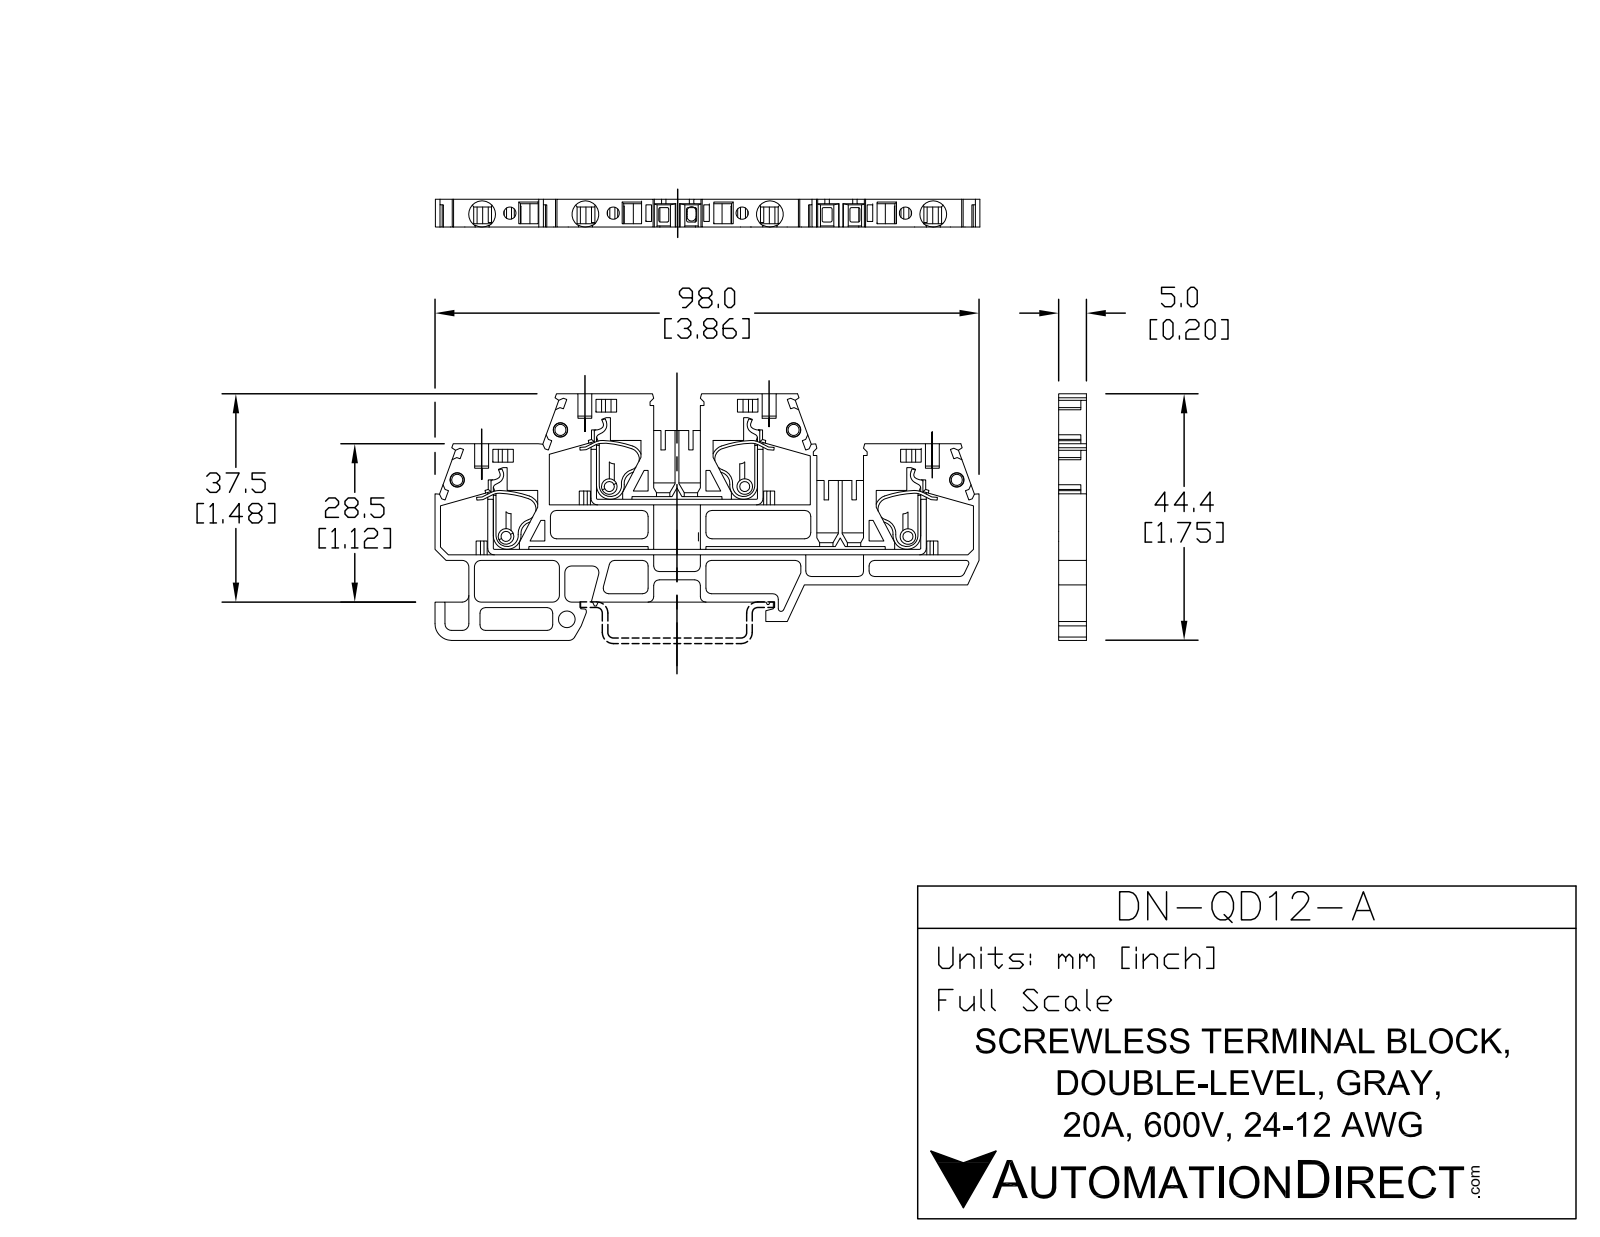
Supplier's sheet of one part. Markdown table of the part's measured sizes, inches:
| quantity | value |
| --- | --- |
| part name | DN-QD12-A |
| STEP written by | SolidWorks 2019 (AUTOMOTIVE_DESIGN) |
| units | inches |
| bodies | 1 solid, 666 faces (536 planar, 101 cylindrical, 29 other) |
| overall size | 3.858 × 1.748 × 0.197 |
| volume | 0.399 in³ |
| surface area | 19.43 in² |
| round holes (diameter × count) | 0.087 × 4, 0.102 × 4, 0.189 × 4, 0.118 × 1 |
| round bosses / shafts (diameter × count) | 0.11 × 4 |
| partial cylindrical surfaces (radius × count) | 0.039 × 23, 0.047 × 12, 0.043 × 8, 0.02 × 4, 0.028 × 4, 0.055 × 4, 0.012 × 1, 0.118 × 1 |
| main face-to-face distances | 0.197, 0.039, 0.031, 0.165, 0.079, 0.118, 0.114, 0.028, 0.394, 0.059 |
| hole center spacings | 0.197, 0.732, 1.11, 1.157, 1.843, 2.268, 3, 0.535 |
